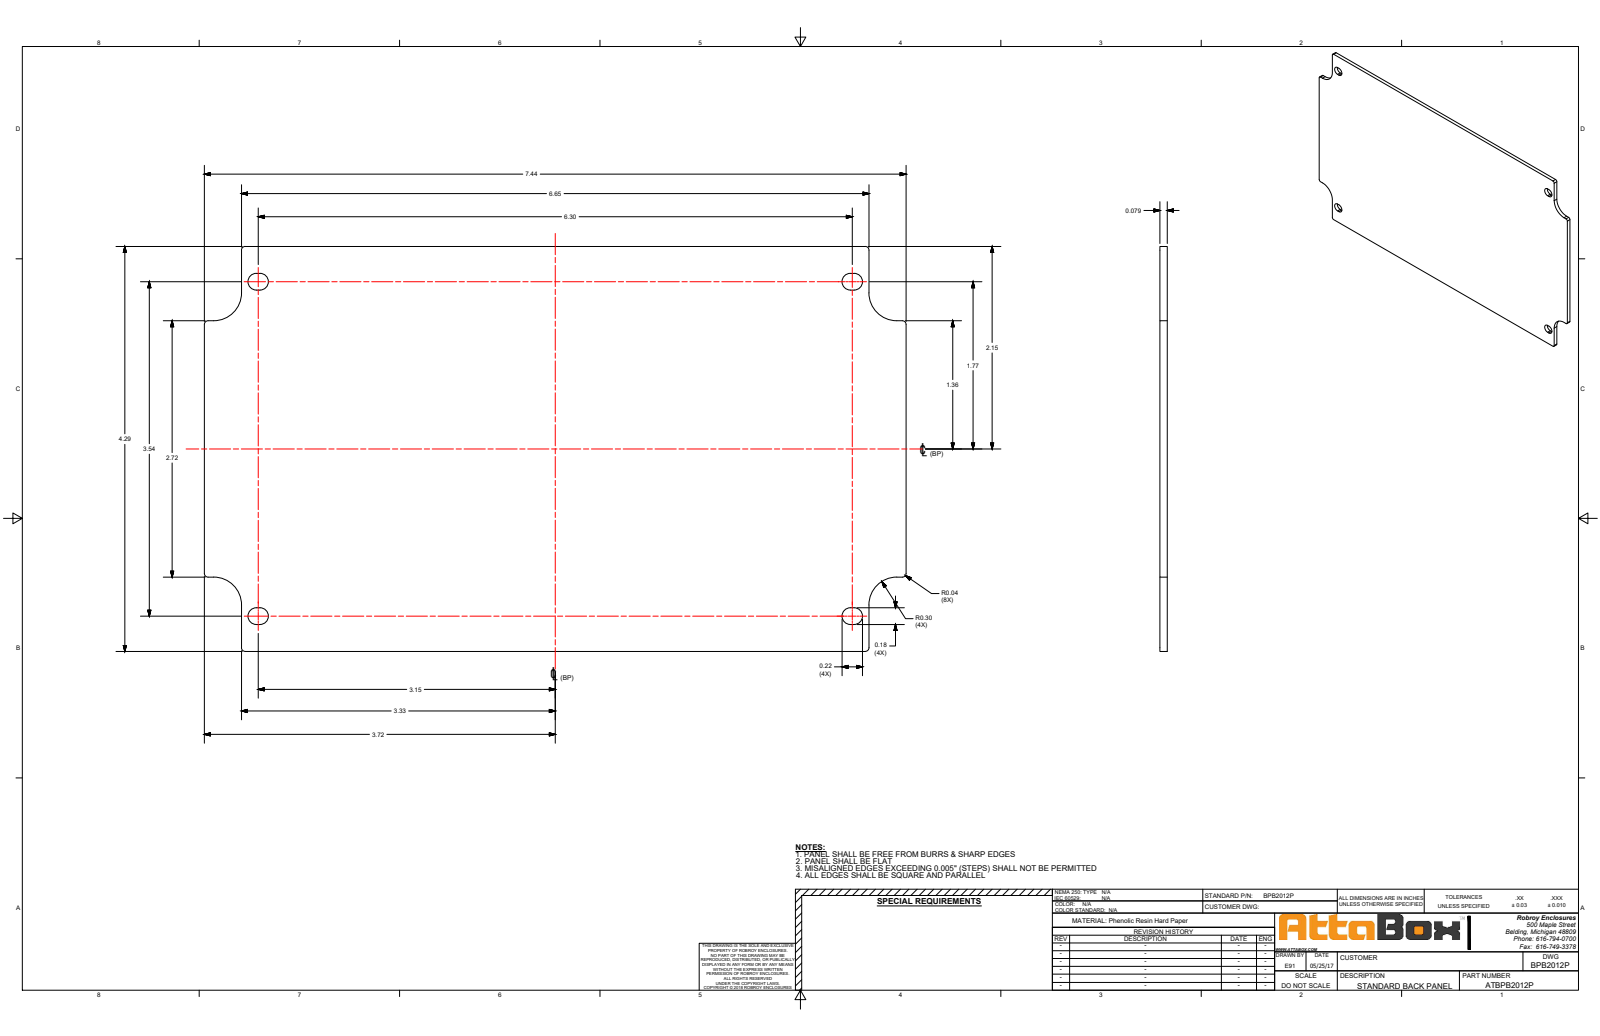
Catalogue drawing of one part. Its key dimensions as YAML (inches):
part_name: "BPB2012P"
step_written_by: "SolidWorks 2018 (AUTOMOTIVE_DESIGN)"
units: inches
bodies: {solids: 1, faces: 42, planar: 22, cylindrical: 20, other: 0}
overall_size: [7.441, 4.291, 0.079]
volume: 2.412
surface_area: 63.27
partial_cylinders:
  - {radius: 0.039, count: 8}
  - {radius: 0.089, count: 8}
  - {radius: 0.295, count: 4}
face_to_face_distances: [0.079, 4.291, 7.441, 0.394, 7.047, 6.654, 0.787, 3.504, 0.285, 0.463]
